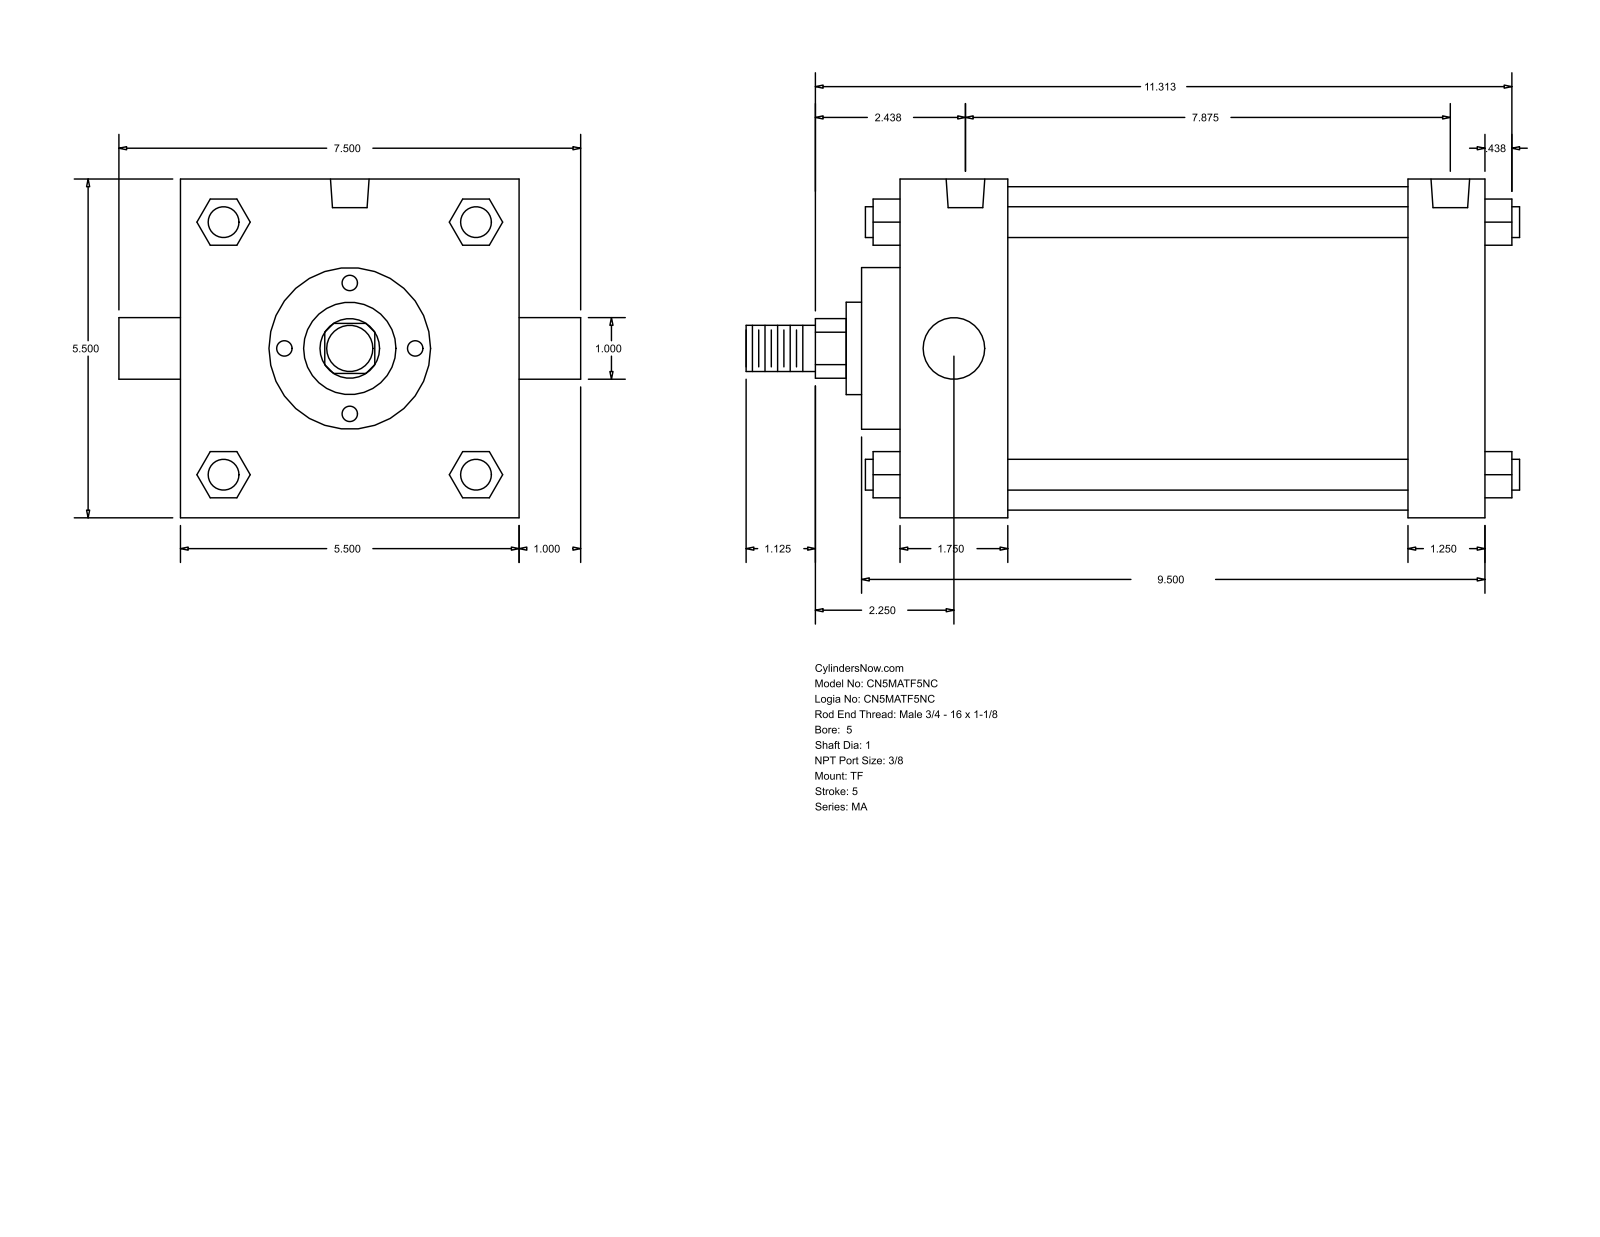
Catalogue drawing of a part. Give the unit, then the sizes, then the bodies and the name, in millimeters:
Units: millimetres
Overall size (bounding box): 319.09 × 190.5 × 139.7
Round holes (diameter × count): ⌀11.11 ×3, ⌀15.93 ×2
Round bosses / shafts (diameter × count): ⌀12.7 ×4, ⌀25.4 ×2, ⌀133.35 ×1, ⌀66.67 ×1, ⌀38.1 ×1, ⌀19.05 ×1
Partial cylindrical surfaces — rounded edges, fillets, slot ends (radius × count): R12.29 ×1
Main face-to-face distances: 139.7, 241.31, 209.55, 31.76, 44.46, 165.09, 196.85, 15.87, 60.33, 225.42
Hole centre spacings: 4.76, 195.27, 190.51, 200.03
Bodies: 0 solids, 122 faces (93 planar, 29 cylindrical, 0 other)
Part name (STEP PRODUCT): MA_TF__0500_1
STEP written by: GSSL Pune (CONFIG_CONTROL_DESIGN)
